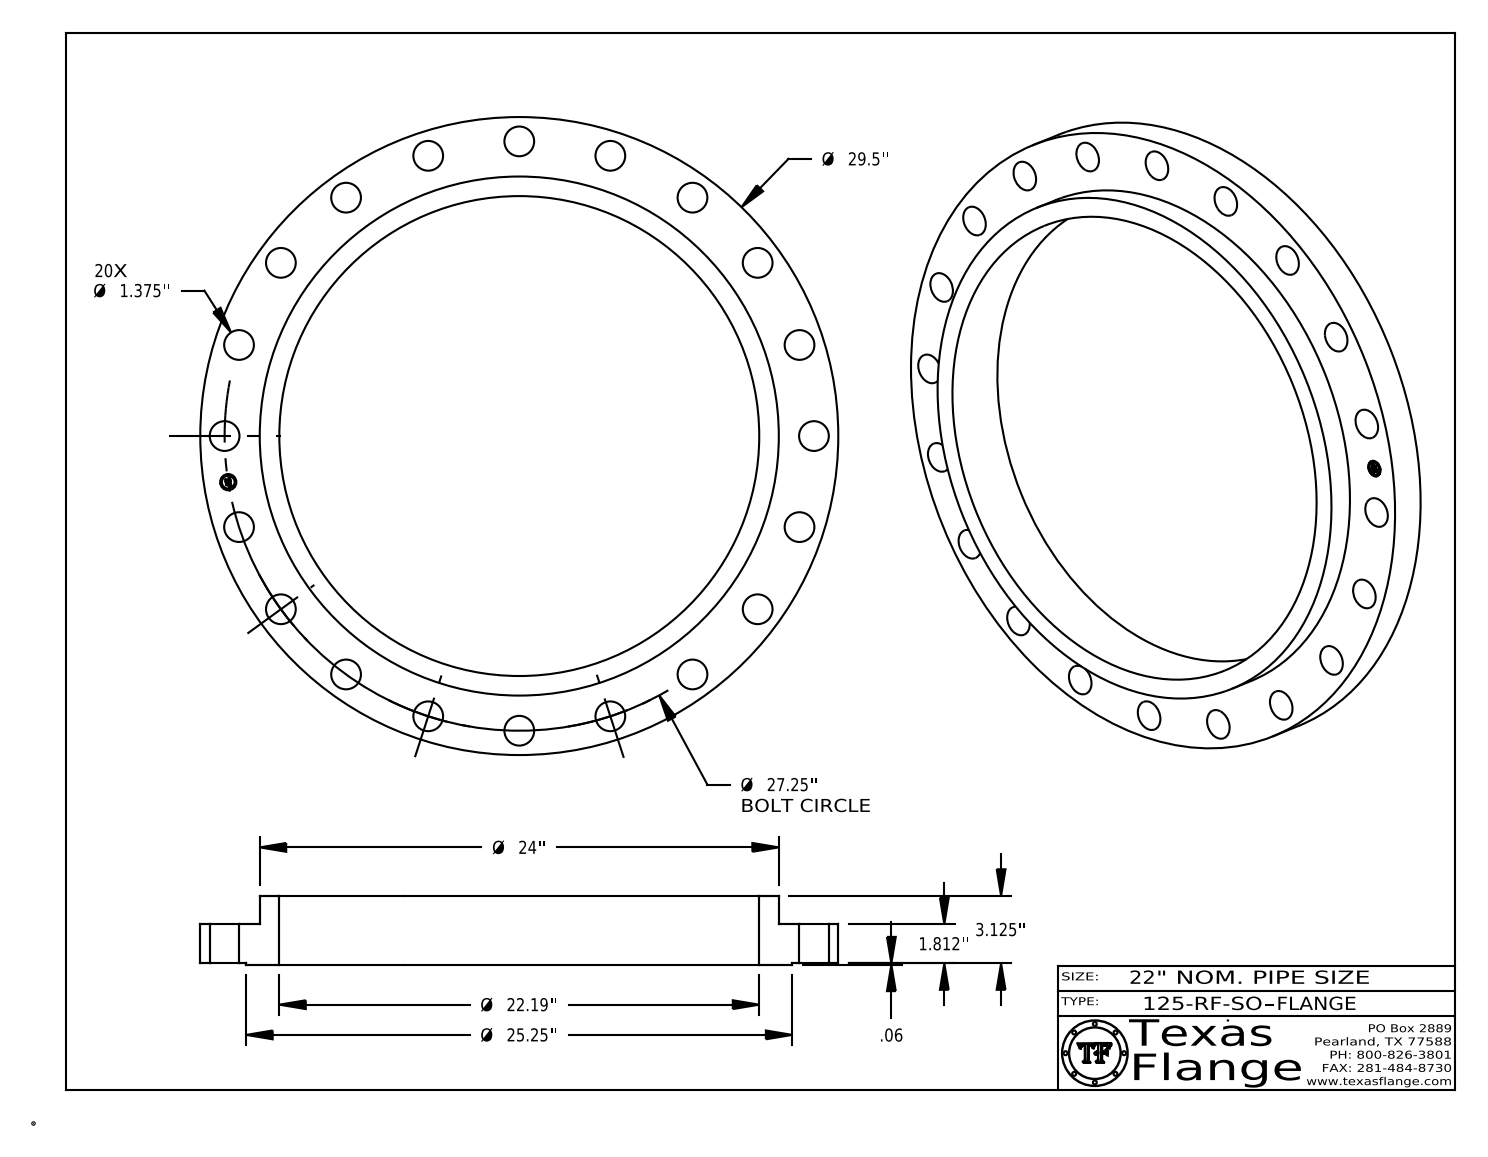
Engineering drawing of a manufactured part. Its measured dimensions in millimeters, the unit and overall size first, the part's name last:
Units: millimetres
Overall size (bounding box): 749.3 × 749.3 × 81
Round holes (diameter × count): ⌀34.9 ×20, ⌀19.1 ×1, ⌀563.6 ×1
Round bosses / shafts (diameter × count): ⌀1.1 ×8, ⌀749.3 ×1, ⌀641.4 ×1, ⌀609.6 ×1, ⌀15 ×1
Main face-to-face distances: 46, 1.6, 47.6, 81, 79.4, 33.4, 47.2, 45.6, 0.4, 33.7
Hole centre spacings: 346.1, 489.4, 658.3, 213.9, 314.2, 108.3, 406.8, 560
Volume: 9 460 000 mm³ · Surface area: 764 500 mm²
Bodies: 1 solid, 437 faces (369 planar, 68 cylindrical, 0 other)
Part name (STEP PRODUCT): 125-RF-SO-B16.1
STEP written by: CATIA V5 STEP AP214 (AUTOMOTIVE_DESIGN)
